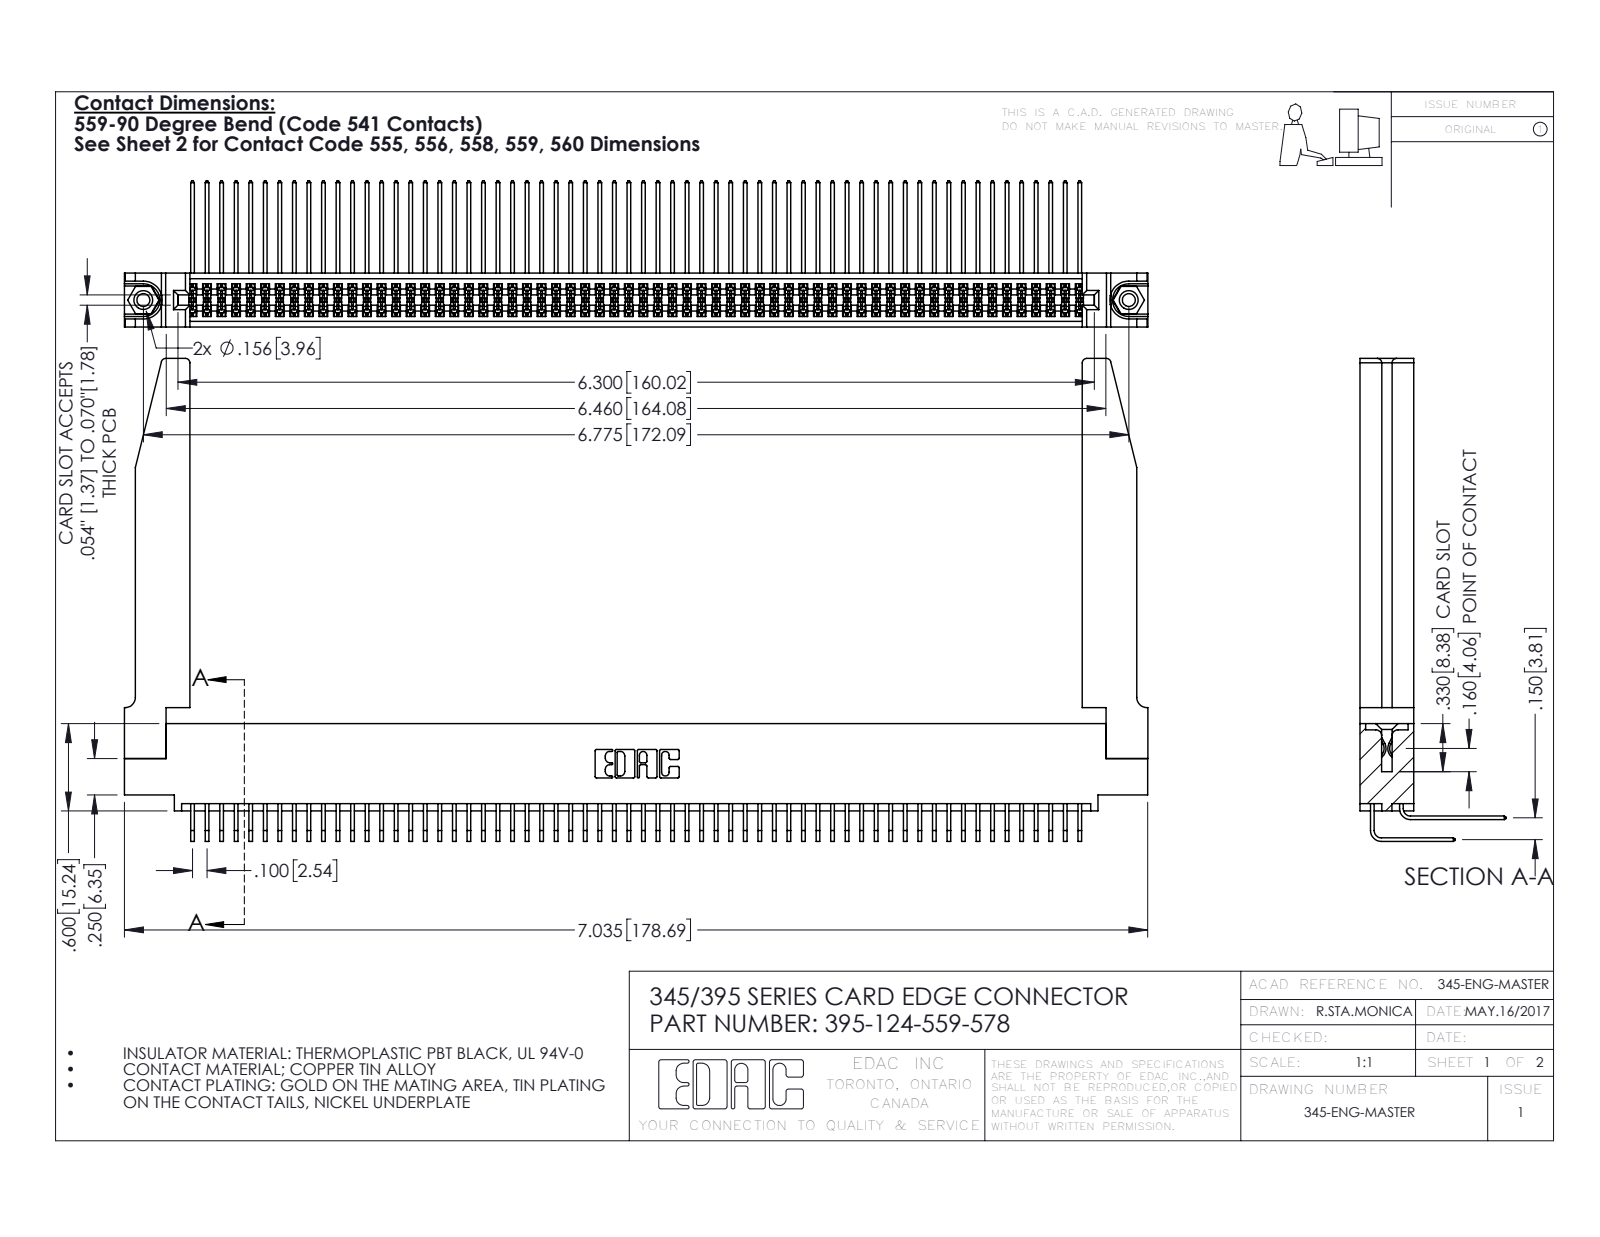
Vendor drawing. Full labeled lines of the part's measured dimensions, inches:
Part name (STEP PRODUCT): 345-292-001_559 Tail - 2; 345-220-078_345-220-078; 345 Part_0.110 Offset - 0.156 Dia-TH; 395-124-559-578 (+2 more)
STEP written by: SolidWorks 2016 (CONFIG_CONTROL_DESIGN)
Units: inches
Bodies: 129 solids, 6812 faces (4566 planar, 2194 cylindrical, 52 other)
Overall size (bounding box): 7.036 × 3.319 × 1.005
Volume: 1.584 in³ · Surface area: 58.23 in²
Round holes (diameter × count): ⌀0.089 ×2, ⌀0.125 ×2, ⌀0.156 ×2, ⌀0.064 ×1
Round bosses / shafts (diameter × count): ⌀0.155 ×2
Partial cylindrical surfaces — rounded edges, fillets, slot ends (radius × count): R0.006 ×186, R0.01 ×22, R0.03 ×8, R0.007 ×6, R0.031 ×6, R0.026 ×3, R0.014 ×2, R0.019 ×2
Main face-to-face distances: 0.072, 0.298, 0.37, 0.098, 0.272, 0.025, 0.2, 0.225, 0.175, 0.15
Hole centre spacings: 0.27, 6.539, 6.775
